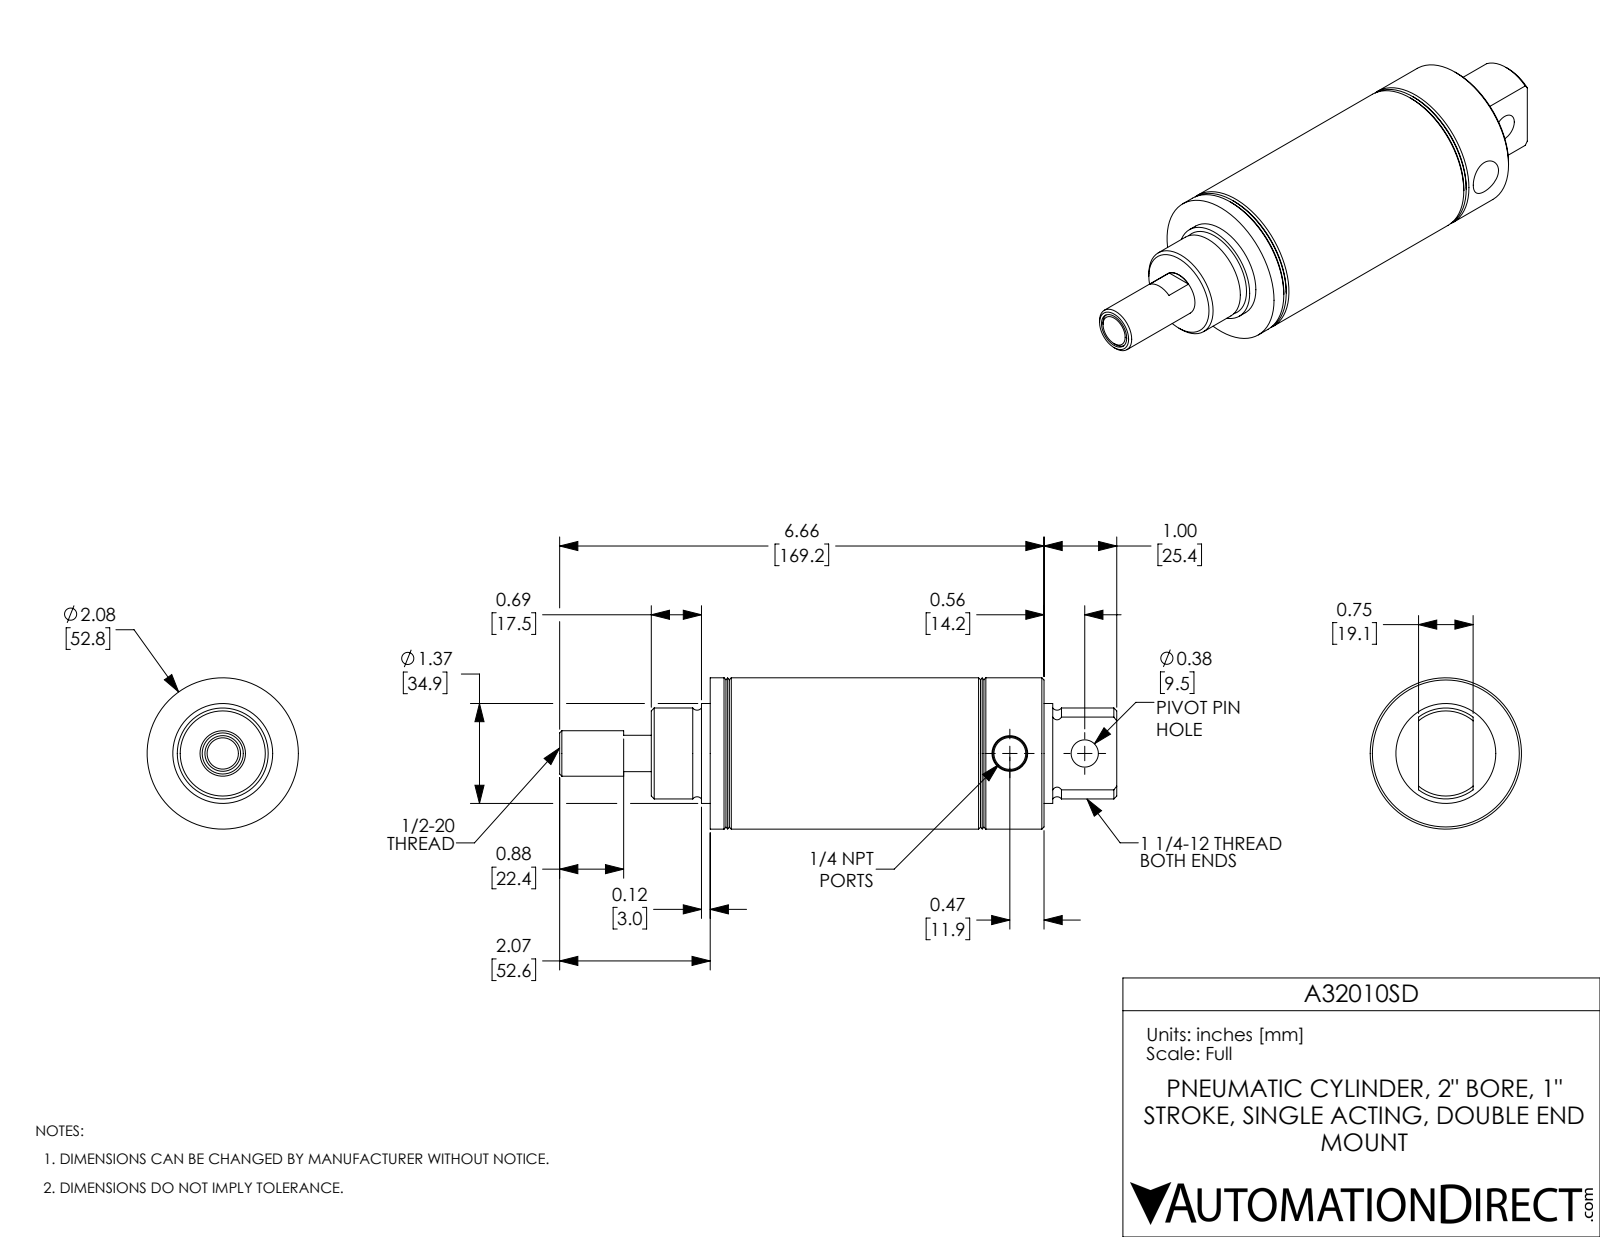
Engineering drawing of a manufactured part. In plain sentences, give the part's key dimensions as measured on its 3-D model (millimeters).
The part is named "A32010SD; A32010SD-Rod; A32010SD-MainBody". Its 3-D file was written by "SolidWorks 2017 (AUTOMOTIVE_DESIGN)". It is 2 solids with 87 faces: 21 planar, 28 cylindrical and 38 other. Overall it measures 194.6 by 52.8 by 52.8 millimeters. Its volume is 243 700 cubic millimeters and its surface area 54 160 square millimeters. Round holes: 1 of diameter 9.5, 1 of diameter 11.1, 1 of diameter 12.5, 1 of diameter 15.9, 1 of diameter 50.8. Round bosses or shafts: 1 of diameter 52.8, 1 of diameter 34.9, 1 of diameter 31.8. The main face-to-face distances are 77.3, 25.4, 39.2, 12.7, 38.1, 64.6, 51.9, 116.6, 3, 42.3. The hole center spacings are 26.2.
